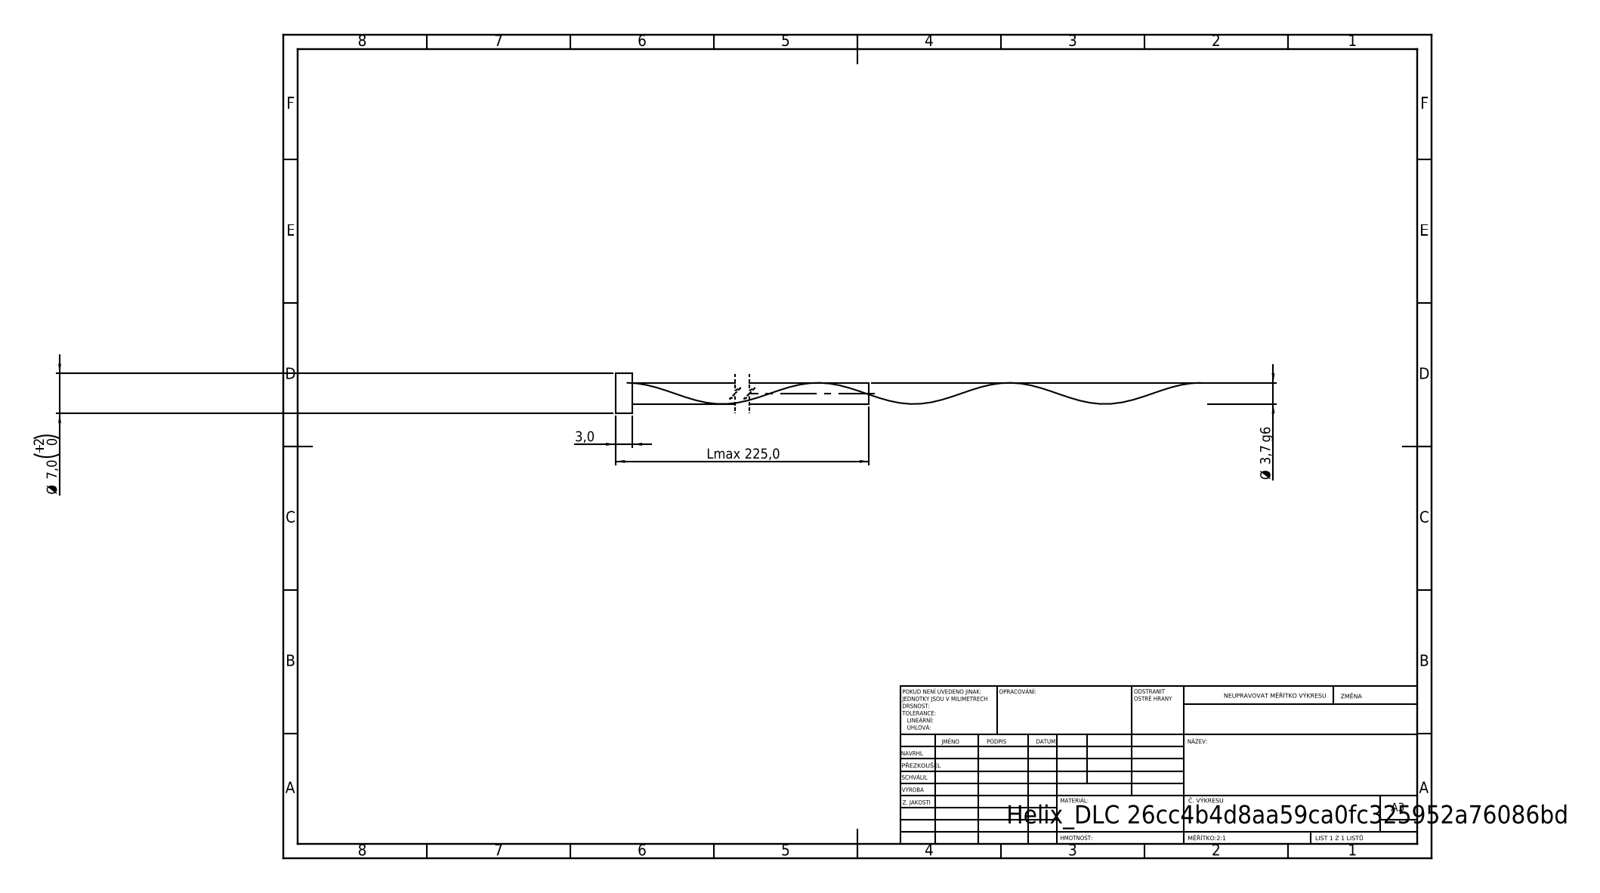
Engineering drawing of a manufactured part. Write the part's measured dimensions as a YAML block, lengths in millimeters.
step_written_by: "SolidWorks 2019 (CONFIG_CONTROL_DESIGN)"
units: millimeters
bodies: {solids: 1, faces: 16, planar: 6, cylindrical: 9, other: 1}
overall_size: [225, 7, 7]
volume: 2957
surface_area: 3543
round_bosses_or_shafts:
  - {diameter: 7, count: 1}
  - {diameter: 3.7, count: 1}
  - {diameter: 2.96, count: 1}
face_to_face_distances: [3, 225, 222, 193.09, 190.09, 31.91, 192.35, 189.35, 0.74, 32.65]
